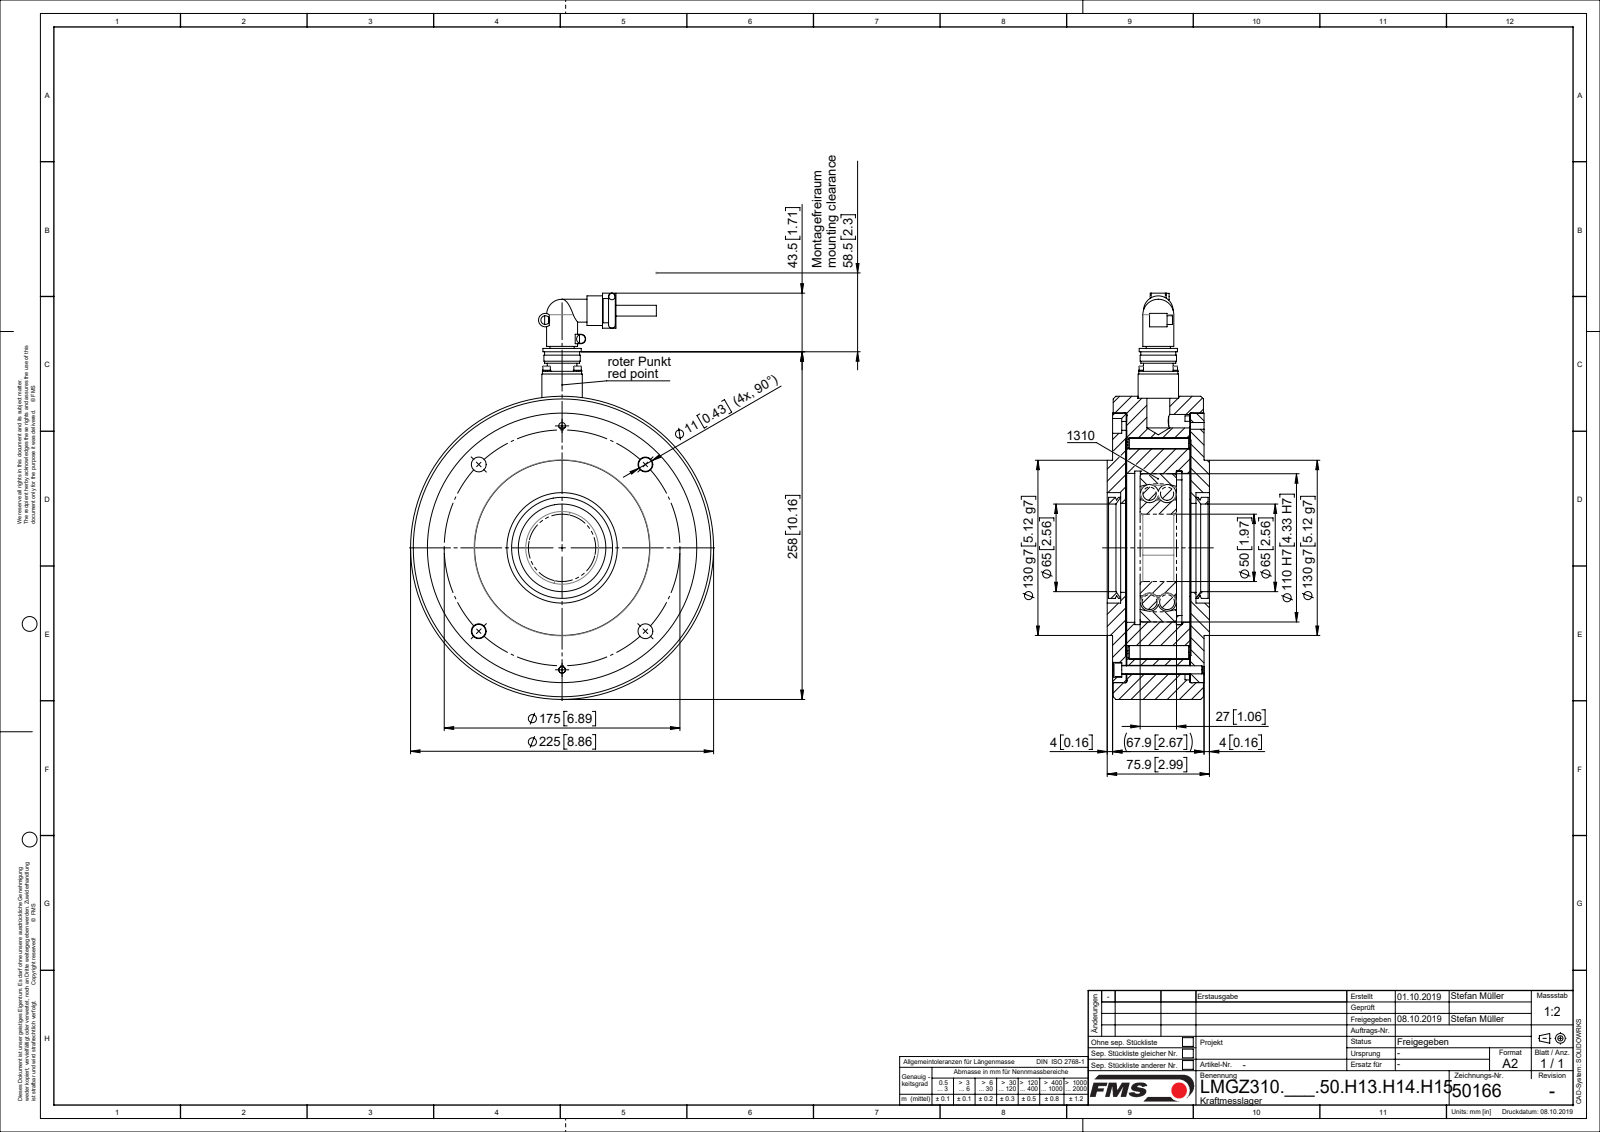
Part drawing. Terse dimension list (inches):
name: L50166; L49152; TEIL1; L49153 (+8 more)
written by: Mechanical Desktop 2007 (CONFIG_CONTROL_DESIGN)
unit: in
bodies: 20 solids, 409 faces (120 planar, 232 cylindrical, 57 other)
size: 11.87 × 8.858 × 2.988
volume: 147.8 in³; area: 606.4 in²
holes: 6× ⌀0.433, 4× ⌀0.102, 4× ⌀0.126, 4× ⌀0.134, 4× ⌀0.138, 4× ⌀0.354, 2× ⌀0.197, 2× ⌀0.26, 1× ⌀0.906, 1× ⌀1.969, 1× ⌀2.52, 1× ⌀2.598
bosses: 4× ⌀0.244, 4× ⌀0.217, 4× ⌀0.118, 2× ⌀0.866, 2× ⌀0.256, 2× ⌀0.189, 1× ⌀8.858, 1× ⌀7.835
rounds: 2× R0.098, 1× R0.138, 1× R0.197, 1× R3.189, 1× R3.386
face distances: 0.382, 1.86, 0.411, 0.423, 1.868, 0.402, 2.262, 2.272, 0.394, 1.85
hole spacings: 0.64, 0.906, 3.445, 1.281, 2.684, 2.684, 3.563, 4.872
